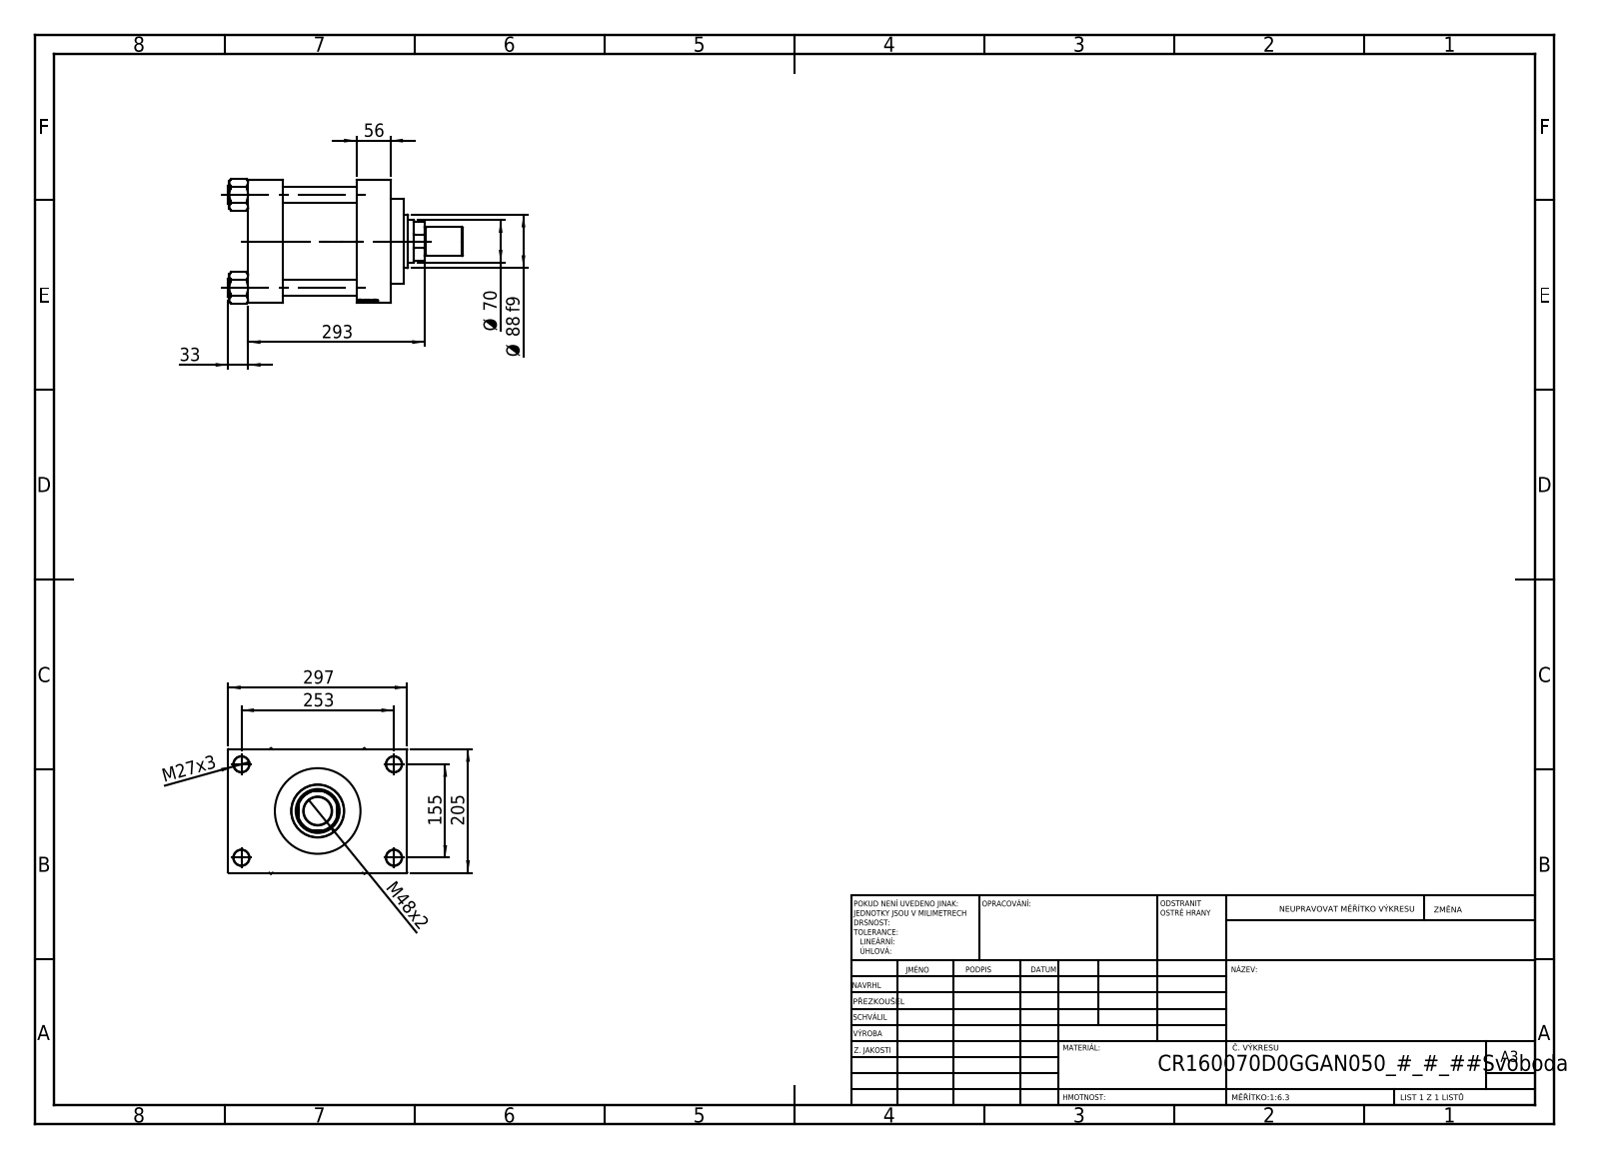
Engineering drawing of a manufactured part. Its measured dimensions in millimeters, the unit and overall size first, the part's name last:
Units: millimetres
Overall size (bounding box): 389 × 297 × 208.14
Round holes (diameter × count): ⌀26 ×4, ⌀27 ×4, ⌀7 ×2, ⌀33.24 ×2, ⌀45 ×2, ⌀46.5 ×1, ⌀70 ×1, ⌀73 ×1, ⌀120 ×1, ⌀142 ×1, ⌀160 ×1
Round bosses / shafts (diameter × count): ⌀30 ×4, ⌀166 ×1, ⌀88 ×1, ⌀48 ×1, ⌀46 ×1
Partial cylindrical surfaces — rounded edges, fillets, slot ends (radius × count): R34 ×1
Main face-to-face distances: 58, 180, 122, 236, 178, 56, 205, 46, 251, 72
Hole centre spacings: 49.05, 109.53, 148.35, 154.9, 162.53, 203.95, 256.13, 155
Volume: 8 240 000 mm³ · Surface area: 785 729 mm²
Bodies: 12 solids, 1163 faces (548 planar, 91 cylindrical, 524 other)
Part name (STEP PRODUCT): ROD_END_AH; V215_VC_A; NUT_M5_D; V215CR_D_Body (+2 more)
STEP written by: SolidWorks 2019 (CONFIG_CONTROL_DESIGN)
